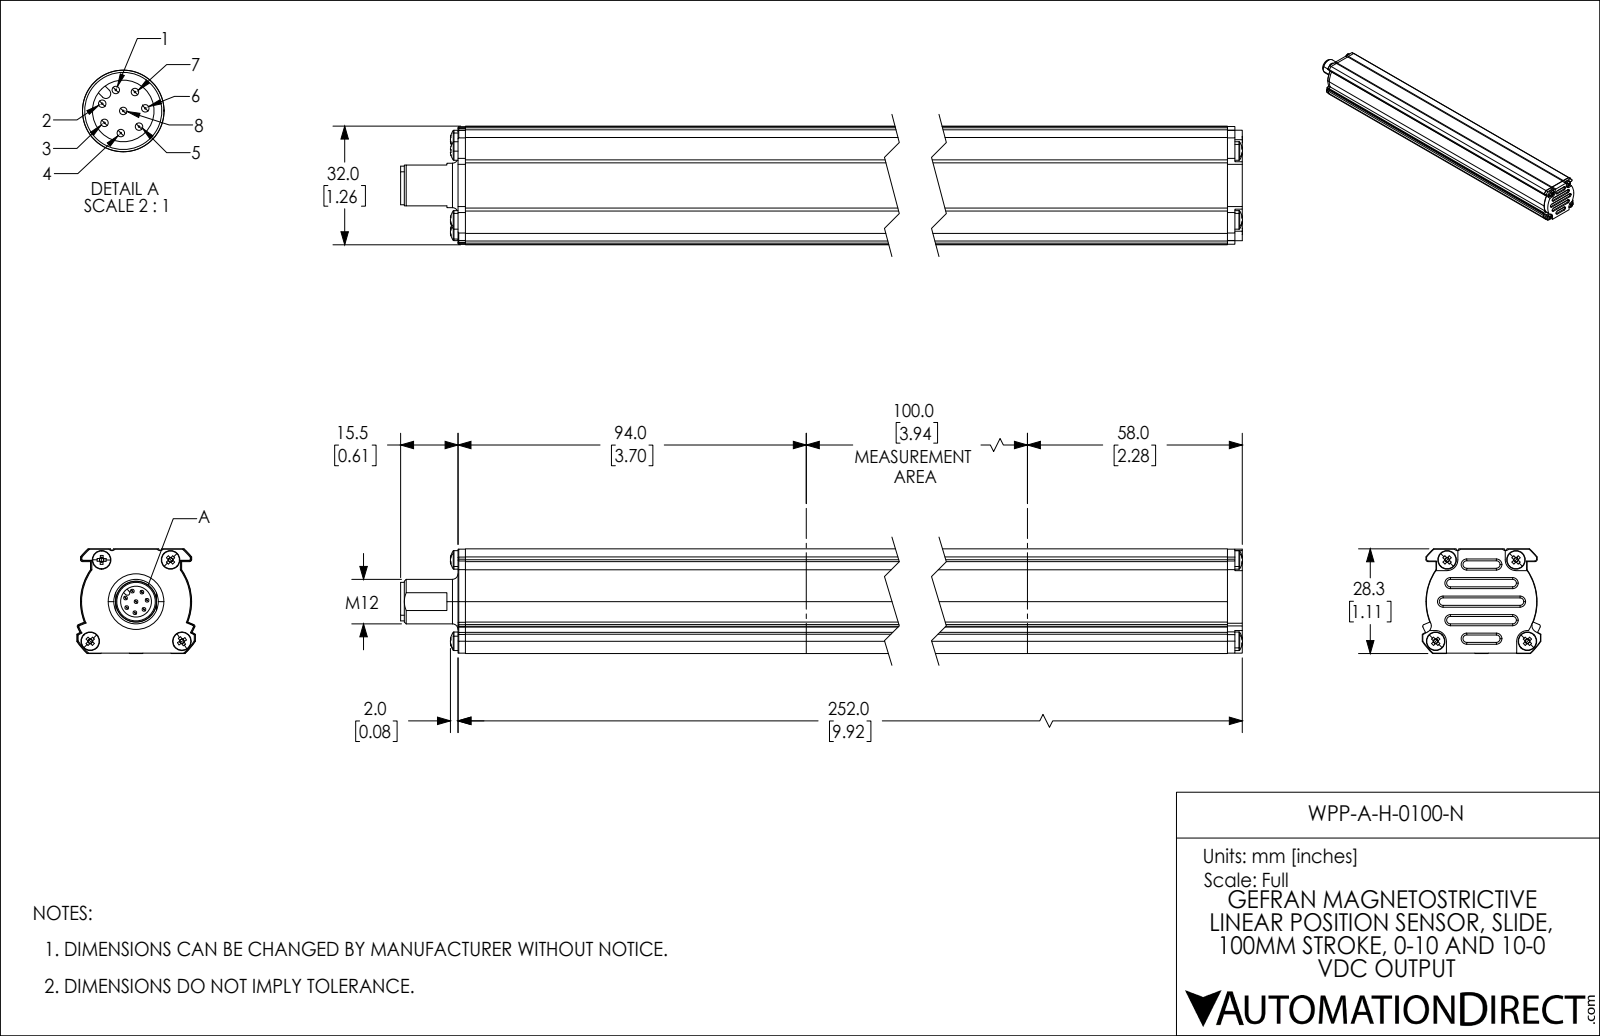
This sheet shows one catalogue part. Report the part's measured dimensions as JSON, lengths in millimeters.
{"part_name": "WPP-A-H-0100-N", "step_written_by": "SolidWorks 2021 (CONFIG_CONTROL_DESIGN)", "units": "millimeters", "bodies": {"solids": 20, "faces": 605, "planar": 301, "cylindrical": 131, "other": 173}, "overall_size": [267.55, 32, 28.25], "volume_mm3": 201518, "surface_area_mm2": 45965, "round_holes": [[2.6, 5], [2.3, 4], [7, 1], [8.3, 1], [9.4, 1]], "round_bosses_or_shafts": [[1, 8], [5, 5], [12, 1], [10.4, 1], [9.55, 1], [8, 1]], "partial_cylinders_radius": [[0.5, 8], [2.9, 4], [0.4, 2], [1, 2], [1.85, 2], [0.65, 1], [2, 1], [14.9, 1]], "face_to_face_distances": [28, 28.25, 246, 2, 24.8, 24.55, 3.45, 3.7, 28.3, 248], "hole_center_spacings": [16.36, 14.6, 22.17, 30.85, 18.6, 22.16, 24.75, 24.76]}
